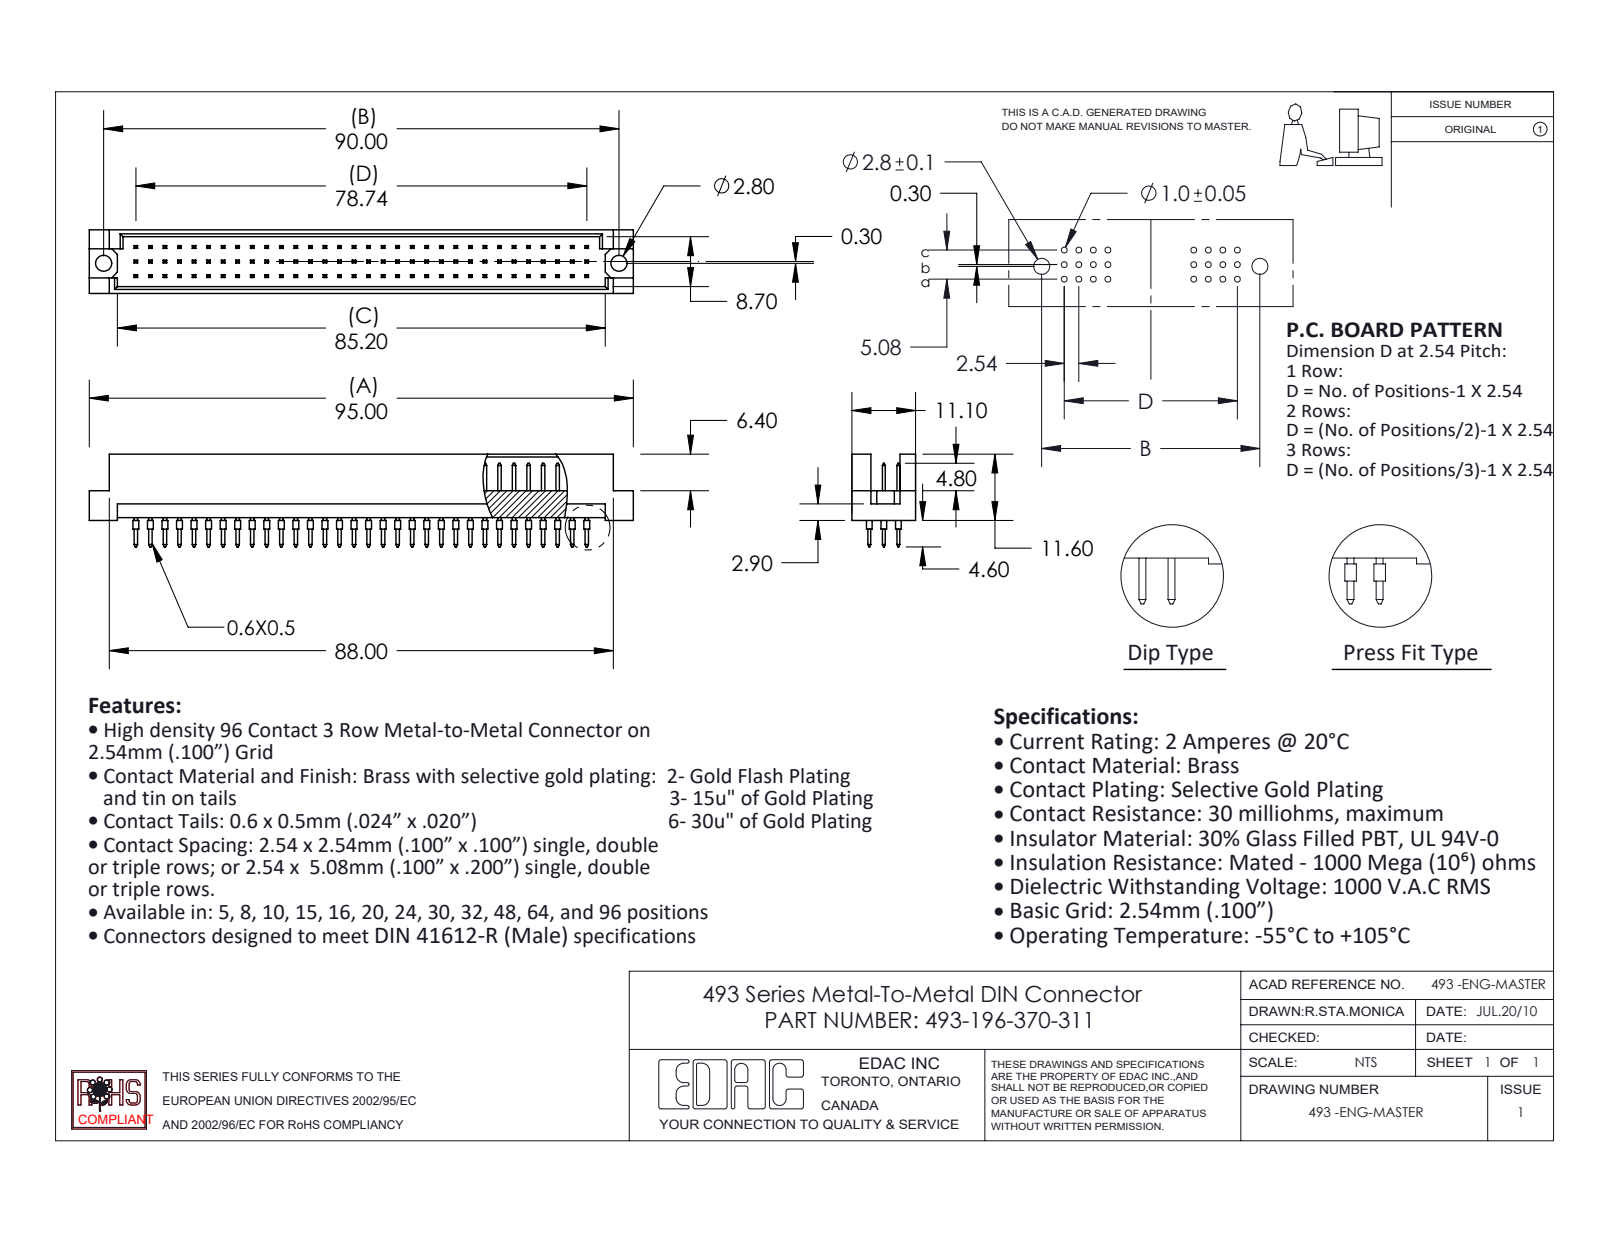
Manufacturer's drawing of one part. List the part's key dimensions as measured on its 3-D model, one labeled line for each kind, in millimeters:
Part name (STEP PRODUCT): 493-196-370-311; 493 Part_96; 493-290_70
STEP written by: SolidWorks 2020 (CONFIG_CONTROL_DESIGN)
Units: millimetres
Bodies: 97 solids, 2548 faces (2352 planar, 196 cylindrical, 0 other)
Overall size (bounding box): 95 × 16.2 × 11.1
Volume: 6 138 mm³ · Surface area: 9 749 mm²
Round holes (diameter × count): ⌀2.8 ×2
Round bosses / shafts (diameter × count): ⌀1 ×96
Main face-to-face distances: 2.54, 1.2, 9.9, 0.5, 5.08, 11.1, 8.7, 4.7, 4.6, 2.76
Hole centre spacings: 90
